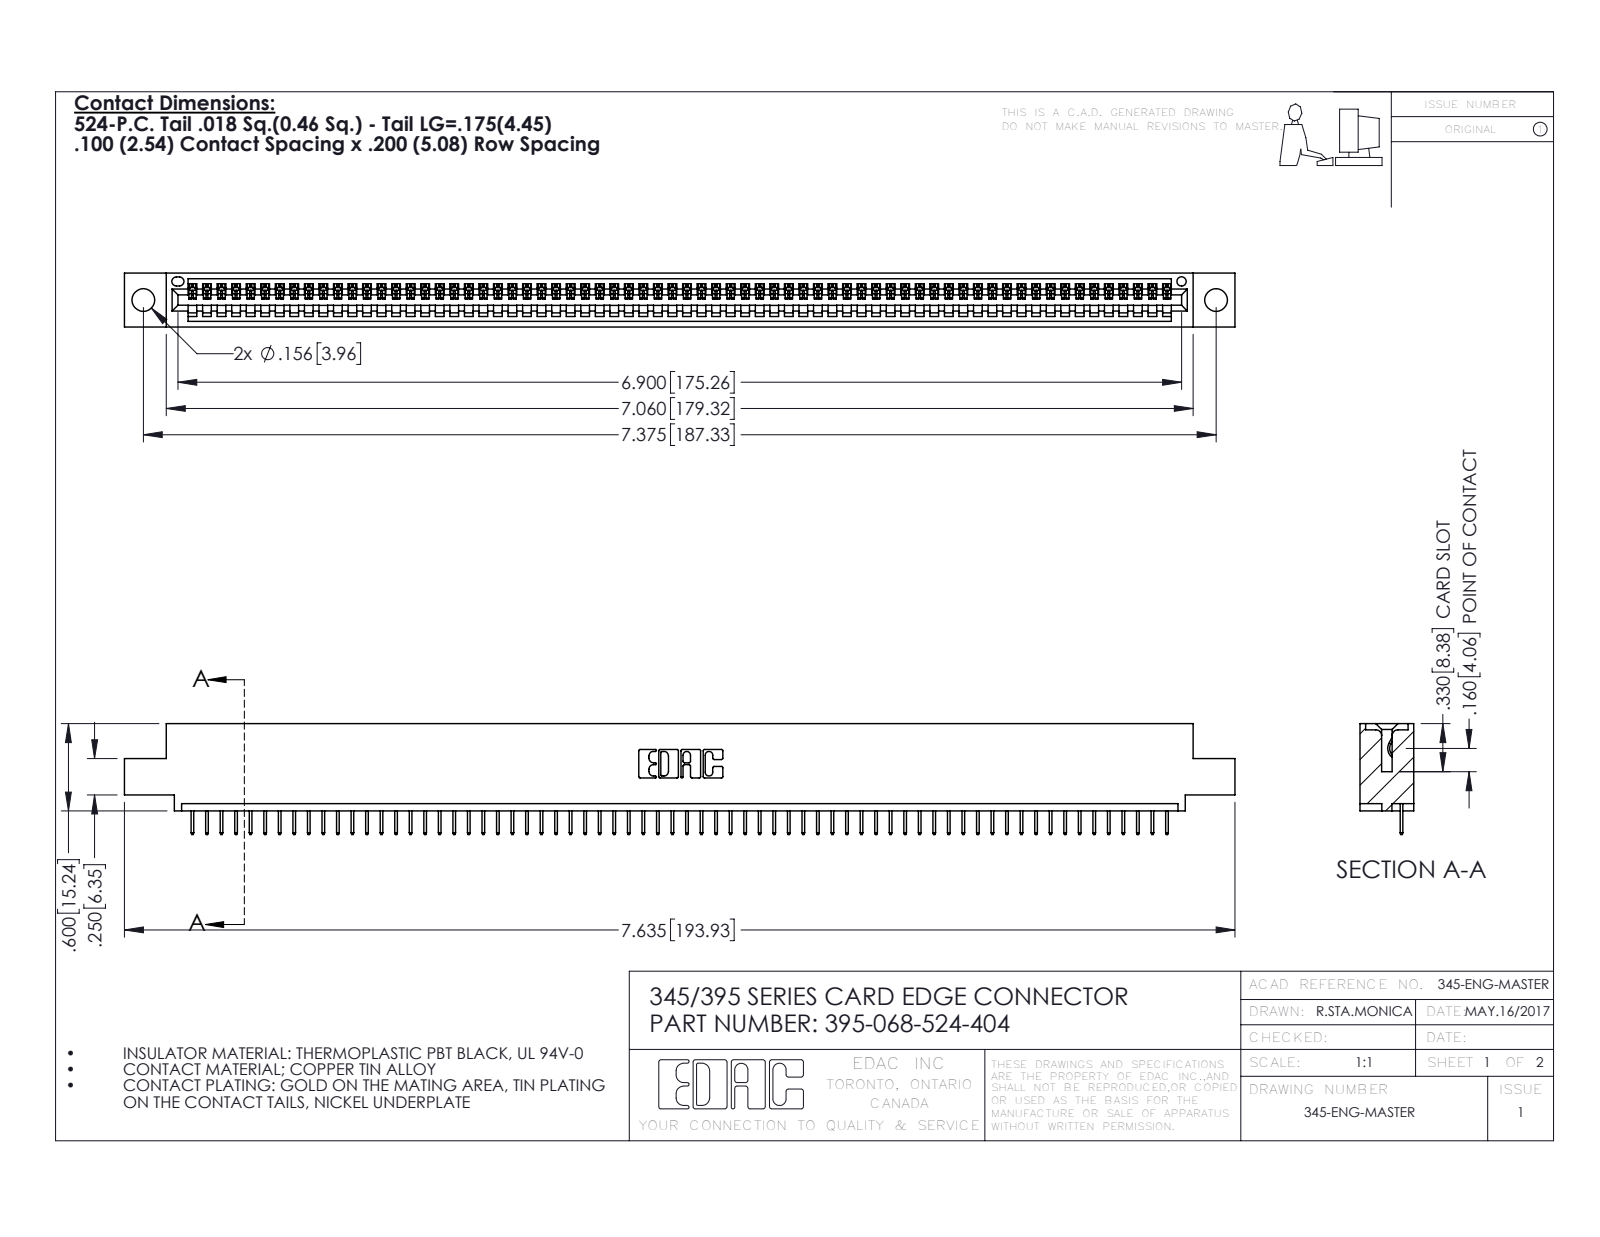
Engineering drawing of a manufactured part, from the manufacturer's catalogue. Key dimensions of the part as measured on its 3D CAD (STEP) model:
Part name (STEP PRODUCT): 395-068-524-404; 345-292-001_345-293-124; 345 Part_0.110 Offset - 0.156 Dia-TH
STEP written by: SolidWorks 2016 (CONFIG_CONTROL_DESIGN)
Units: inches
Bodies: 69 solids, 4346 faces (3212 planar, 1134 cylindrical, 0 other)
Overall size (bounding box): 7.635 × 0.762 × 0.37
Volume: 1.111 in³ · Surface area: 36.54 in²
Round holes (diameter × count): ⌀0.156 ×2, ⌀0.064 ×1
Partial cylindrical surfaces — rounded edges, fillets, slot ends (radius × count): R0.006 ×136, R0.01 ×22, R0.007 ×6, R0.031 ×6, R0.026 ×3, R0.031 ×2, R0.04 ×2, R0.014 ×1
Main face-to-face distances: 0.072, 0.298, 0.37, 0.2, 0.098, 0.272, 0.025, 0.225, 0.072, 0.149
Hole centre spacings: 0.27, 7.139, 7.375
